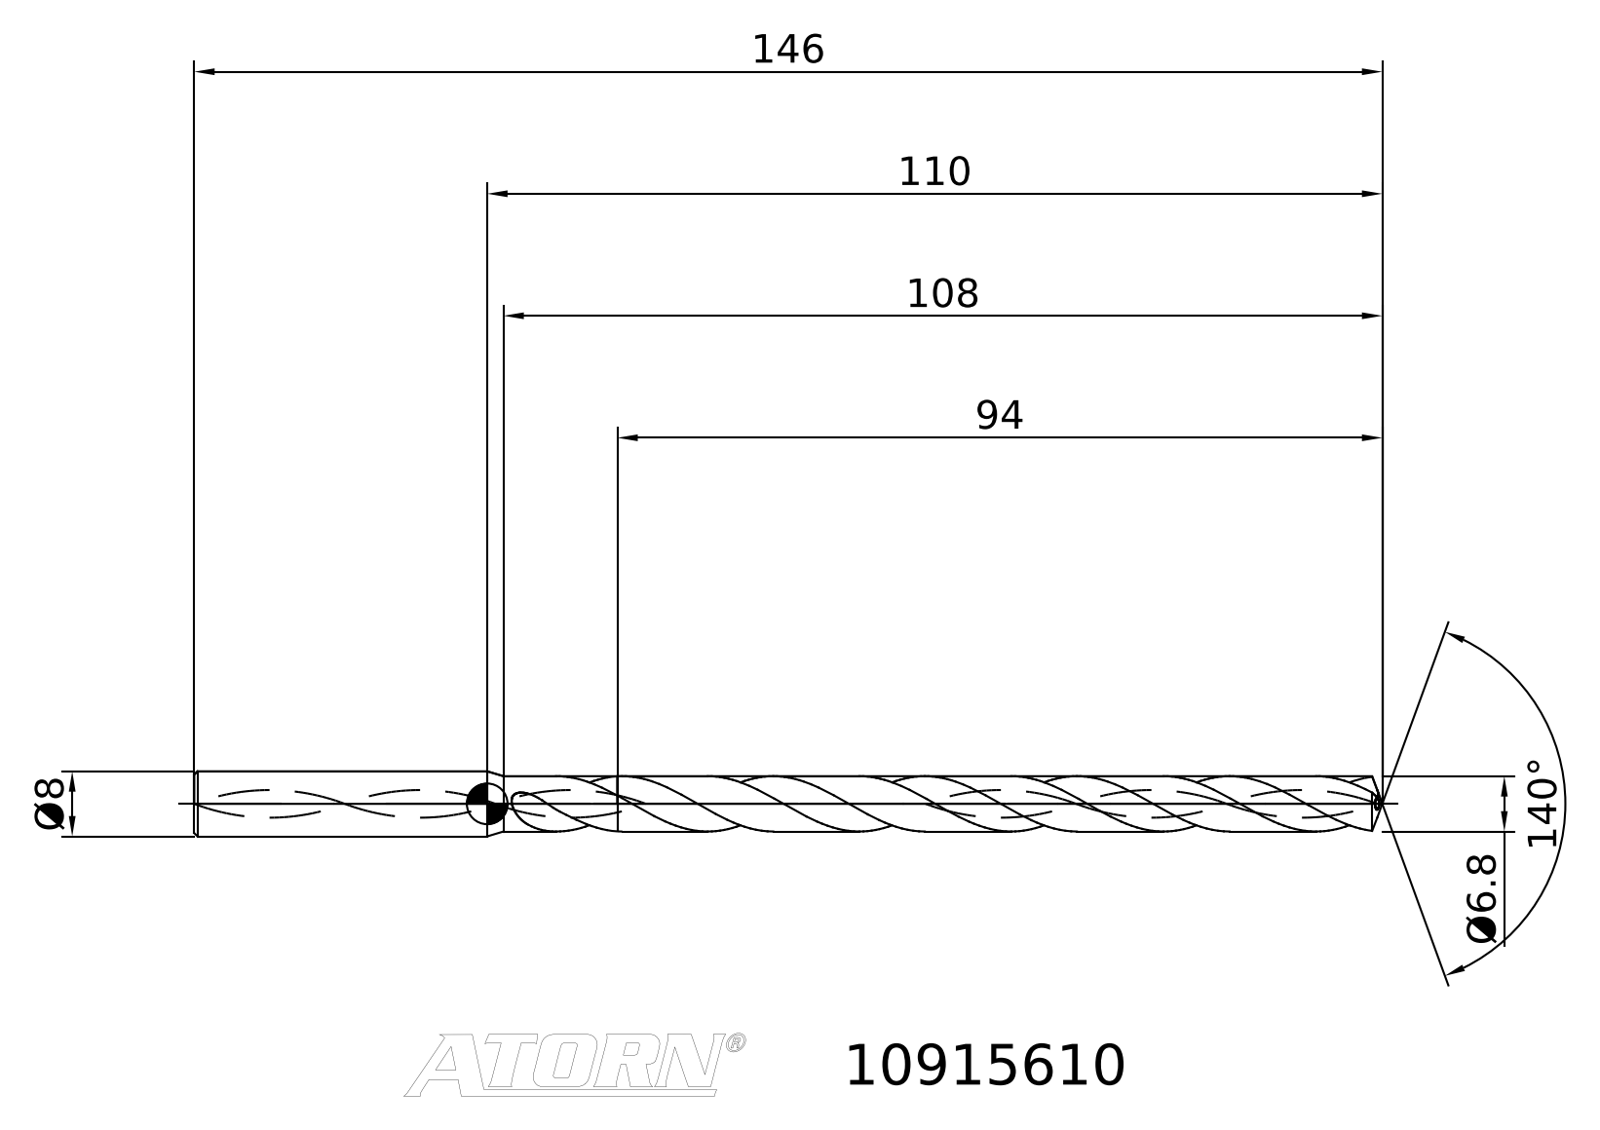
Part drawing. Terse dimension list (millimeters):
written by: TDM (AUTOMOTIVE_DESIGN)
unit: mm
bodies: 2 solids, 35 faces (5 planar, 0 cylindrical, 30 other)
size: 146 × 11.87 × 8
volume: 4 455 mm³; area: 3 593 mm²
face distances: 52, 93.07, 145.07
